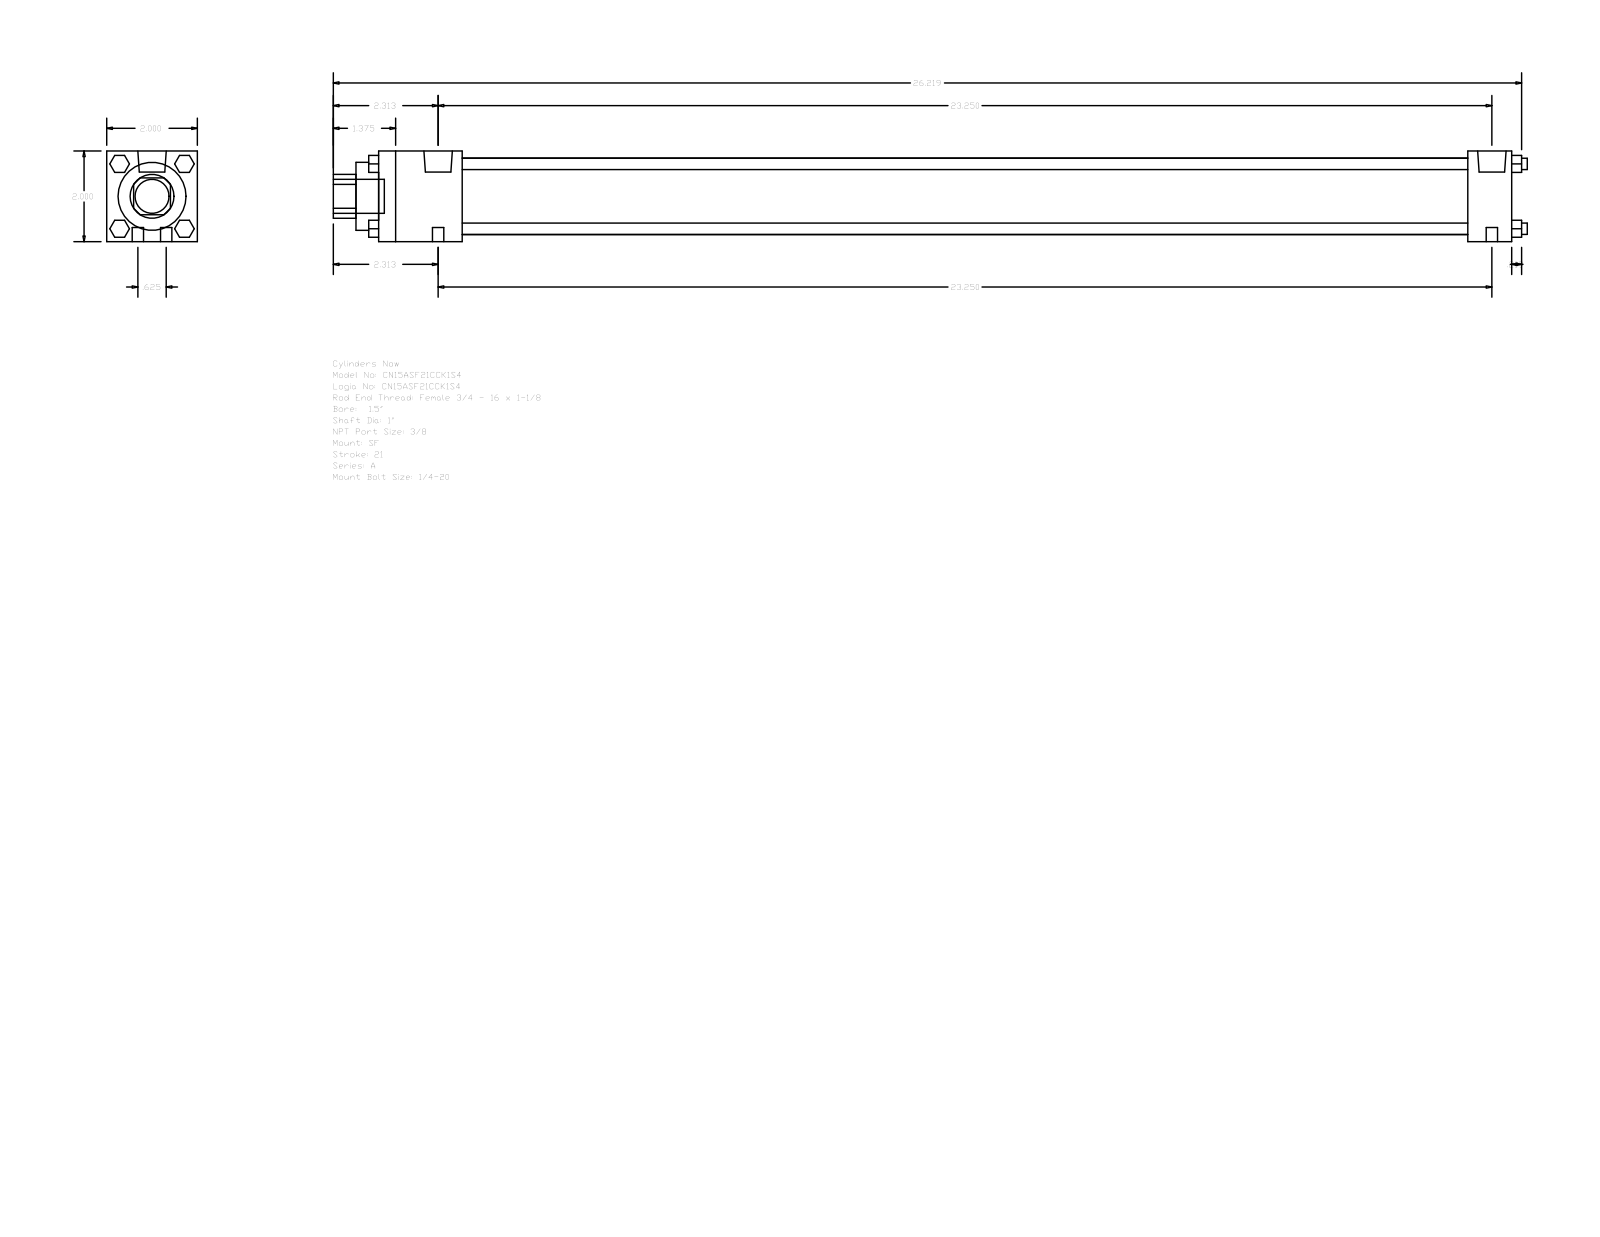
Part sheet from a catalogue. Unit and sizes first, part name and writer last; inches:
Units: inches
Overall size (bounding box): 26.344 × 2 × 2
Round holes (diameter × count): ⌀1 ×1, ⌀1.5 ×1, ⌀1.69 ×1
Round bosses / shafts (diameter × count): ⌀0.25 ×8, ⌀0.627 ×2, ⌀0.219 ×2, ⌀0.75 ×1
Partial cylindrical surfaces — rounded edges, fillets, slot ends (radius × count): R0.484 ×1
Main face-to-face distances: 2, 25, 1.844, 24.031, 22.187, 23.156, 0.969, 0.5, 2.344, 24.531
Bodies: 0 solids, 124 faces (94 planar, 30 cylindrical, 0 other)
Part name (STEP PRODUCT): A_SF__0150_1
STEP written by: GSSL Pune (CONFIG_CONTROL_DESIGN)
